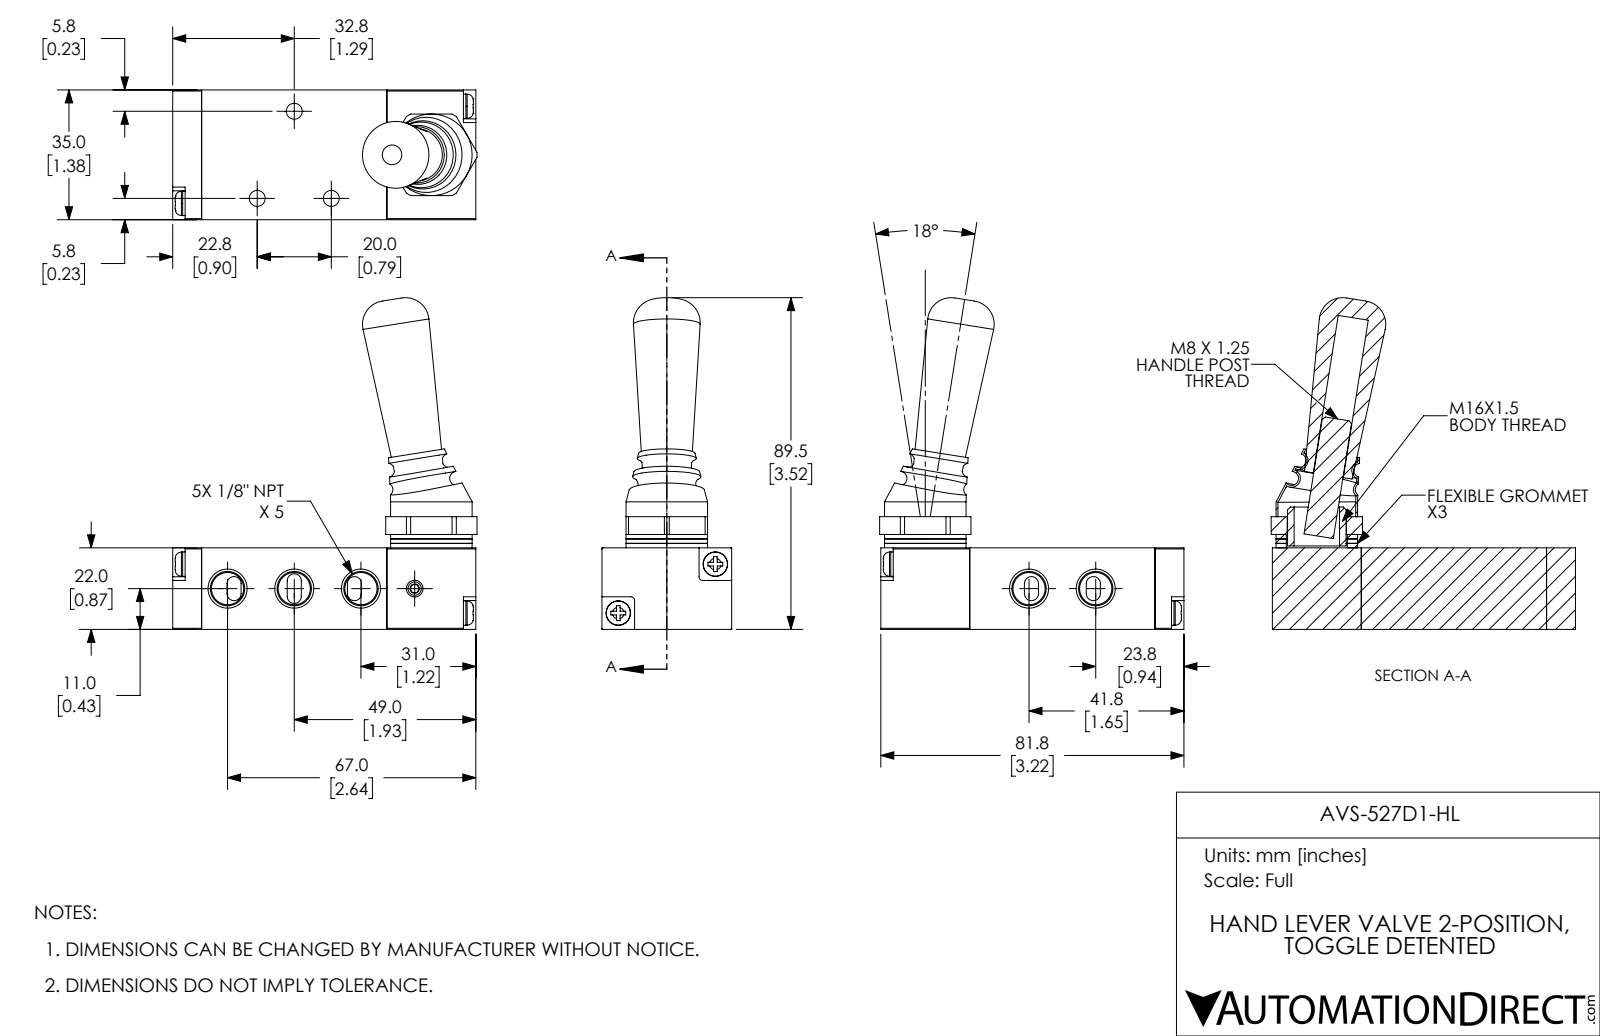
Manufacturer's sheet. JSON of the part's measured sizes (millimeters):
{"part_name": "AVS-527D1-HL", "step_written_by": "SolidWorks 2015 (CONFIG_CONTROL_DESIGN)", "units": "millimeters", "bodies": {"solids": 4, "faces": 245, "planar": 133, "cylindrical": 57, "other": 55}, "overall_size": [94, 84.9, 35], "volume_mm3": 72100, "surface_area_mm2": 21080, "round_holes": [[4.3, 3], [4.5, 1]], "round_bosses_or_shafts": [[6.6, 4], [6.5, 4], [20, 1], [10, 1], [3.6, 1]], "partial_cylinders_radius": [[1.9, 10], [0.3, 4], [1, 4]], "face_to_face_distances": [22, 50, 35, 70, 6.7, 20, 76.7, 56.7, 3.4, 8.8], "hole_center_spacings": [25.6, 20]}
